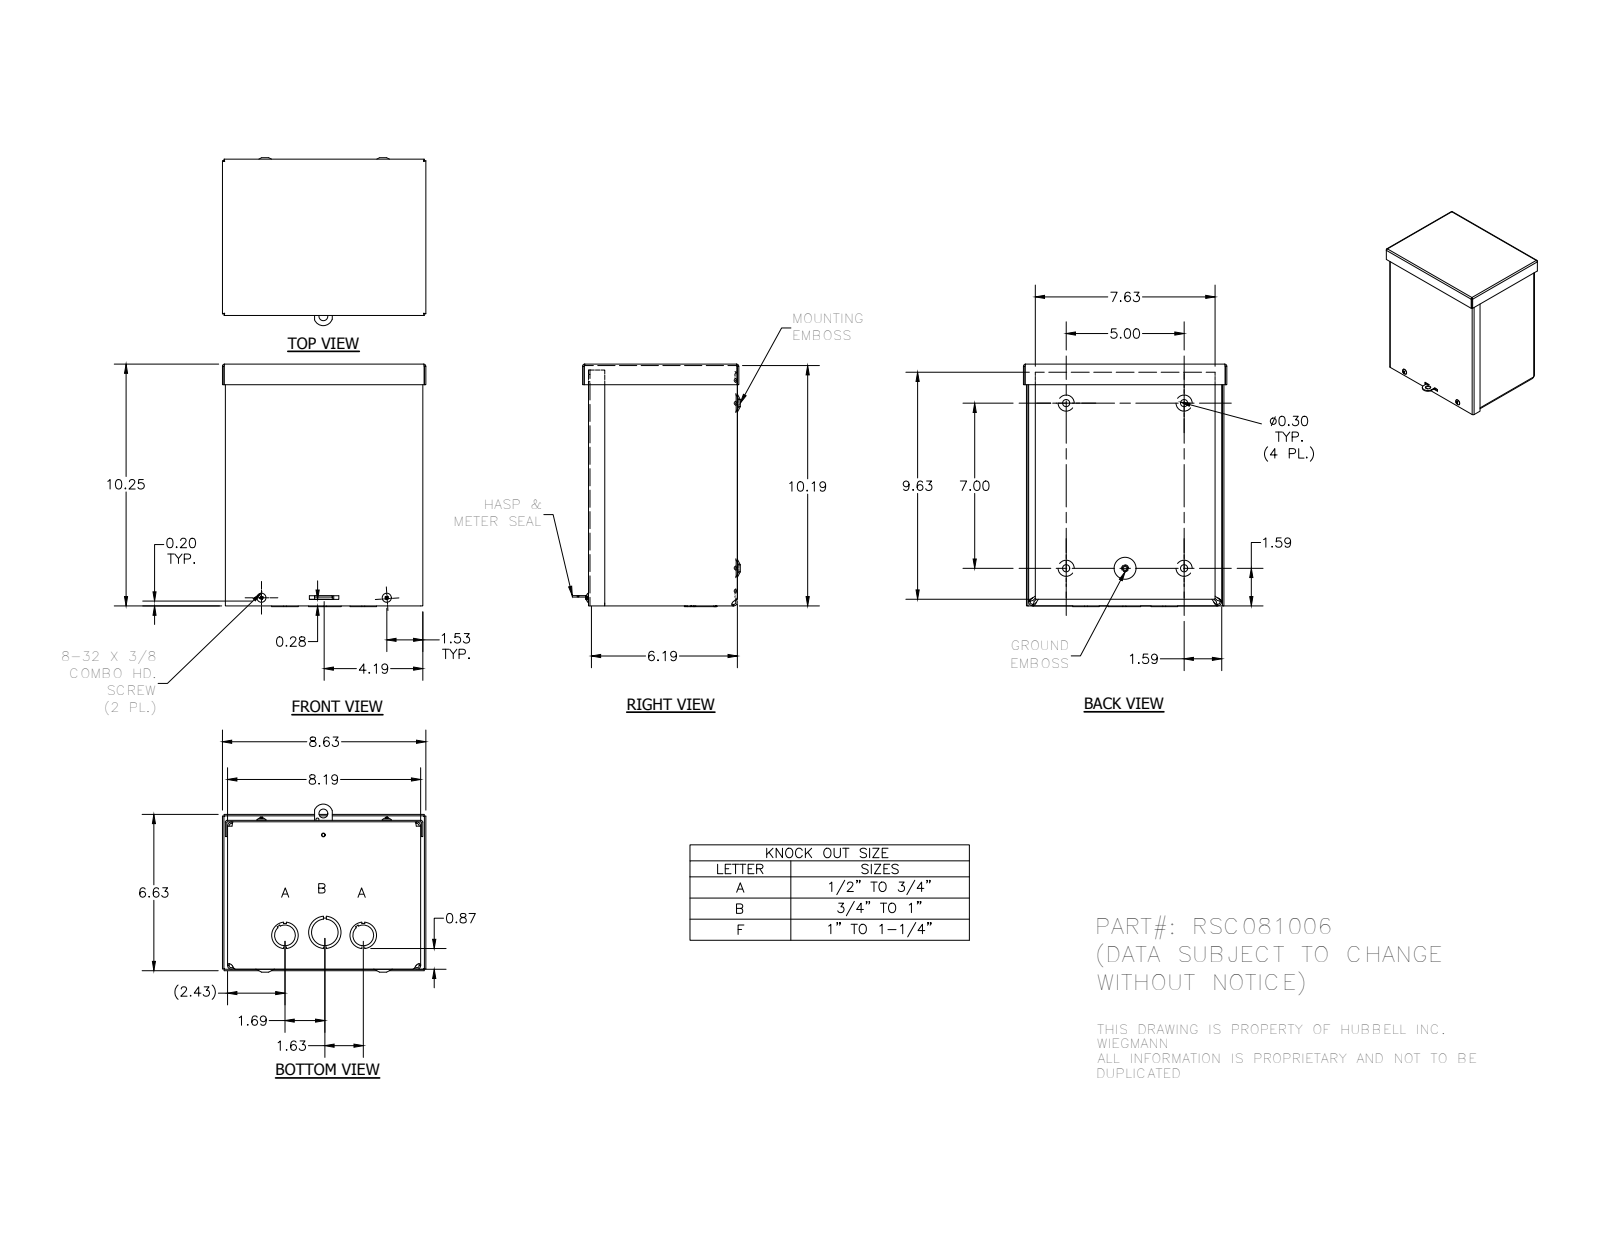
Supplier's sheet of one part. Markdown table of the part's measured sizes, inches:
| quantity | value |
| --- | --- |
| part name | RSC081006; RSC081006_WRAP; RSC0810_LID; RSC0806_CAP (+4 more) |
| STEP written by | Autodesk Inventor 2012 (AUTOMOTIVE_DESIGN) |
| units | inches |
| bodies | 7 solids, 503 faces (238 planar, 121 cylindrical, 144 other) |
| overall size | 10.281 × 8.625 × 7.125 |
| volume | 32.59 in³ |
| surface area | 1 066 in² |
| round holes (diameter × count) | 0.3 × 4, 0.313 × 4, 1.125 × 3, 0.125 × 2, 0.148 × 2, 0.875 × 2, 0.156 × 1, 0.165 × 1, 0.375 × 1, 1.375 × 1 |
| round bosses / shafts (diameter × count) | 0.384 × 2, 0.164 × 2, 0.229 × 1 |
| partial cylindrical surfaces (radius × count) | 0.01 × 10, 0.031 × 8, 0.093 × 8, 0.125 × 8, 0.187 × 8, 0.021 × 4, 0.031 × 4, 0.055 × 4 |
| main face-to-face distances | 0.062, 0.062, 8.126, 6.249, 10.126, 6.187, 0.063, 0.124, 6.312, 6.25 |
| hole center spacings | 1.072, 1.261, 2.5, 5, 5.313, 7, 7.433, 8.063 |
